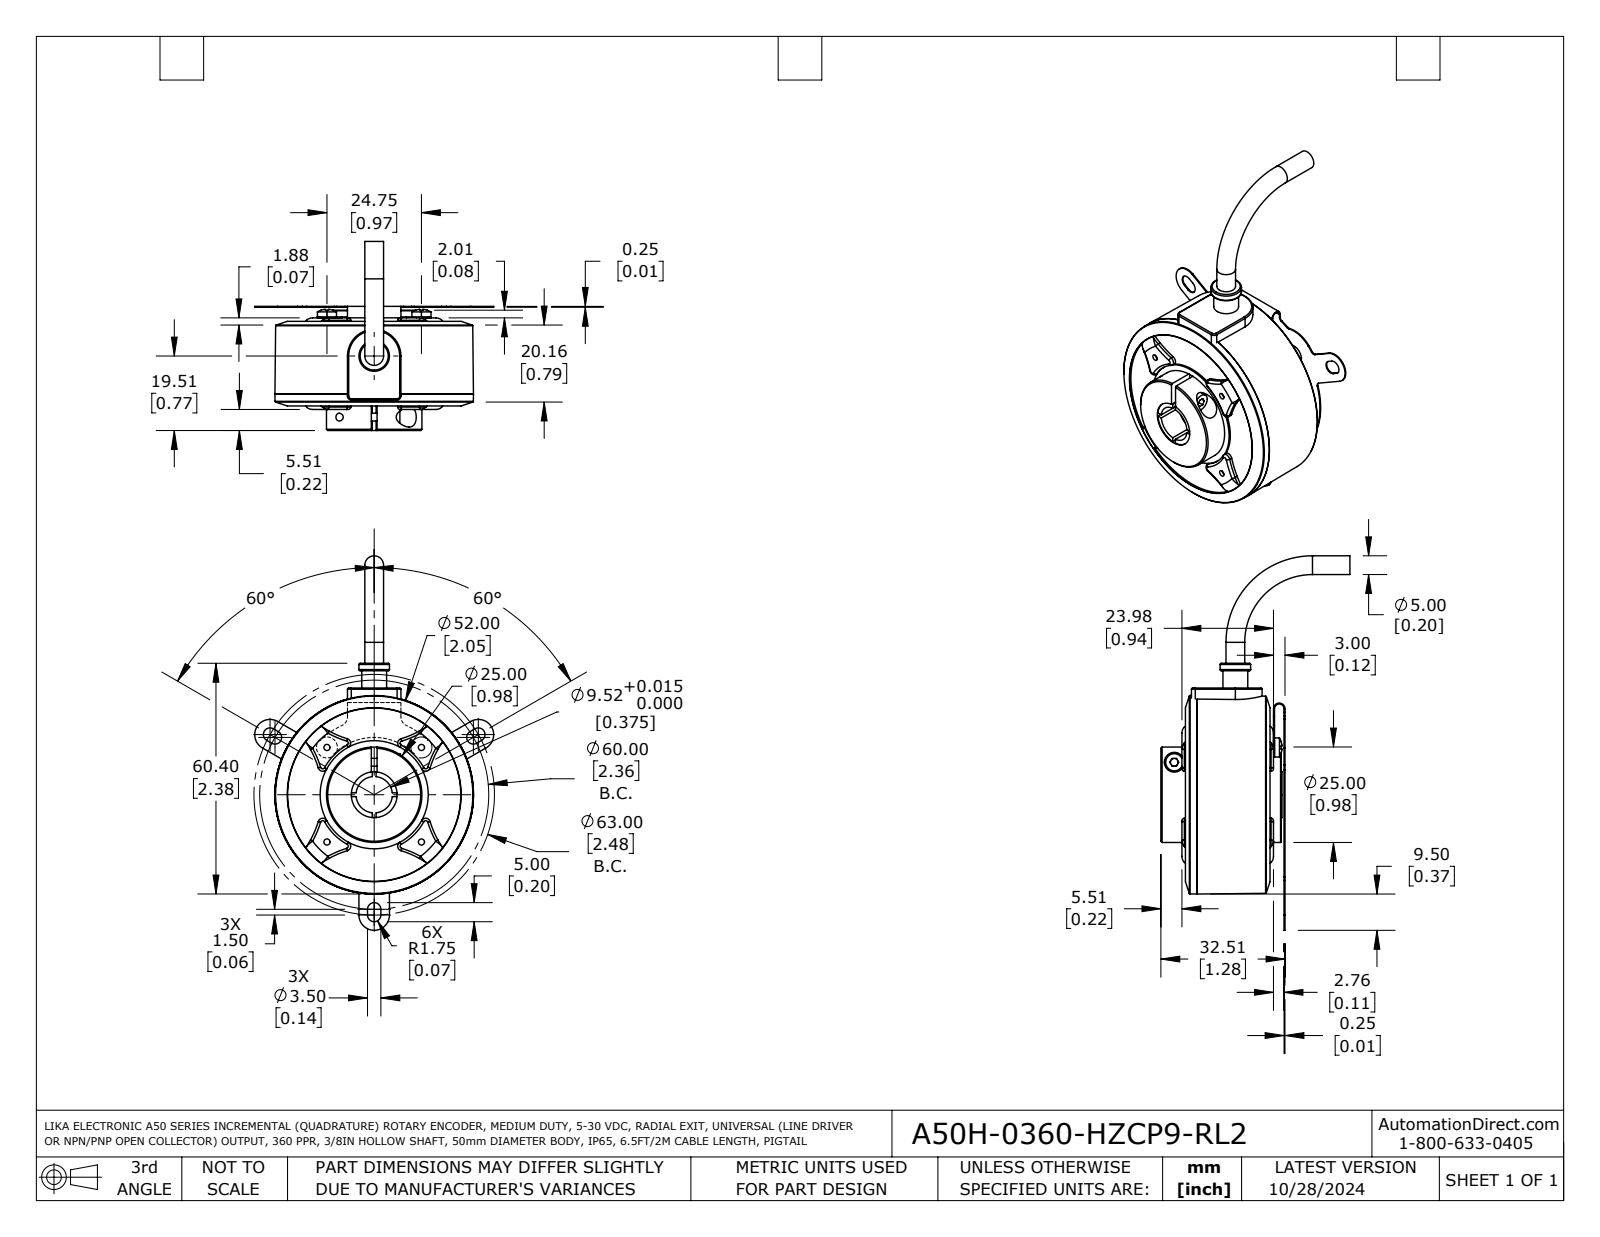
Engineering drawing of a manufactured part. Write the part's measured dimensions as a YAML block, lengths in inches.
part_name: "A50H-0360-HZCP9-RL25"
step_written_by: "SolidWorks 2021 (AUTOMOTIVE_DESIGN)"
units: inches
bodies: {solids: 8, faces: 504, planar: 168, cylindrical: 160, other: 176}
overall_size: [3.86, 2.464, 1.949]
volume: 3.657
surface_area: 31.76
round_holes:
  - {diameter: 0.064, count: 4}
  - {diameter: 0.11, count: 3}
  - {diameter: 0.217, count: 2}
  - {diameter: 0.081, count: 1}
  - {diameter: 0.205, count: 1}
  - {diameter: 0.375, count: 1}
  - {diameter: 0.472, count: 1}
  - {diameter: 1.024, count: 1}
  - {diameter: 1.115, count: 1}
  - {diameter: 1.786, count: 1}
round_bosses_or_shafts:
  - {diameter: 0.098, count: 4}
  - {diameter: 0.197, count: 2}
  - {diameter: 0.193, count: 2}
  - {diameter: 0.984, count: 1}
  - {diameter: 0.315, count: 1}
  - {diameter: 0.256, count: 1}
  - {diameter: 0.177, count: 1}
partial_cylinders:
  - {radius: 0.039, count: 12}
  - {radius: 0.008, count: 8}
  - {radius: 0.008, count: 6}
  - {radius: 0.069, count: 6}
  - {radius: 0.157, count: 3}
  - {radius: 0.01, count: 2}
  - {radius: 0.013, count: 2}
  - {radius: 0.098, count: 2}
face_to_face_distances: [0.896, 0.906, 0.154, 0.144, 0.751, 1.009, 0.999, 0.854, 0.103, 0.709]
hole_center_spacings: [0.583, 0.689, 0.974, 1.383, 0.807, 1.378, 1.614]
